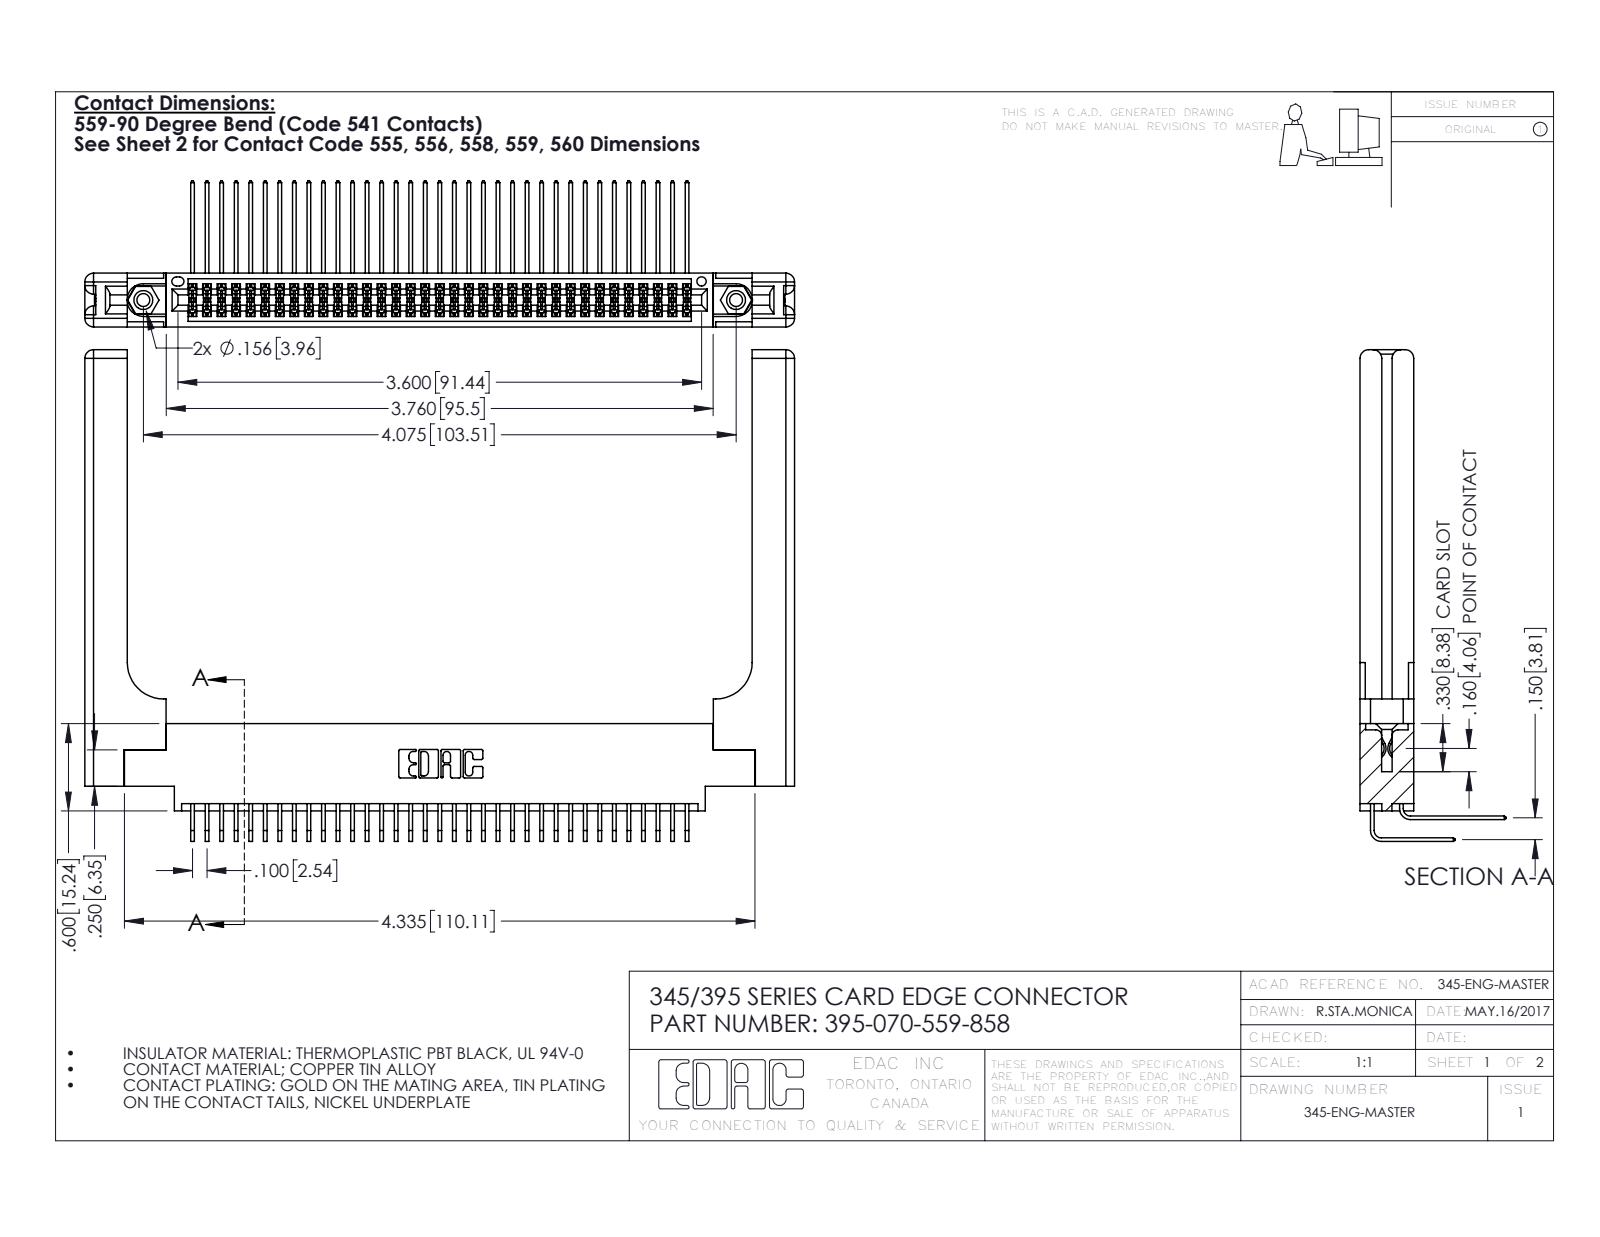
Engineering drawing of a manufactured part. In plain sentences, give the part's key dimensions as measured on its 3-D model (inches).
The part is named "345-292-001_558 559 Tail - 1; 345-250-001_345-250-001-102; 395-070-559-858; 345-220-058_345-220-058 (+2 more)". Its 3-D file was written by "SolidWorks 2016 (CONFIG_CONTROL_DESIGN)". It is 75 solids with 4026 faces: 2682 planar, 1284 cylindrical and 60 other. Overall it measures 4.879 by 3.379 by 1.005 inches. Its volume is 1.266 cubic inches and its surface area 38.9 square inches. Round holes: 2 of diameter 0.089, 2 of diameter 0.125, 2 of diameter 0.156, 1 of diameter 0.064. Round bosses or shafts: 2 of diameter 0.155. Partial cylindrical surfaces (rounded edges, fillets, slot ends): 105 of radius 0.006, 22 of radius 0.01, 16 of radius 0.06, 6 of radius 0.007, 6 of radius 0.031, 3 of radius 0.026, 2 of radius 0.014, 2 of radius 0.019. The main face-to-face distances are 0.37, 0.072, 0.298, 0.098, 0.272, 0.025, 0.2, 0.225, 0.15, 0.175. The hole center spacings are 0.27, 3.839, 4.075.
